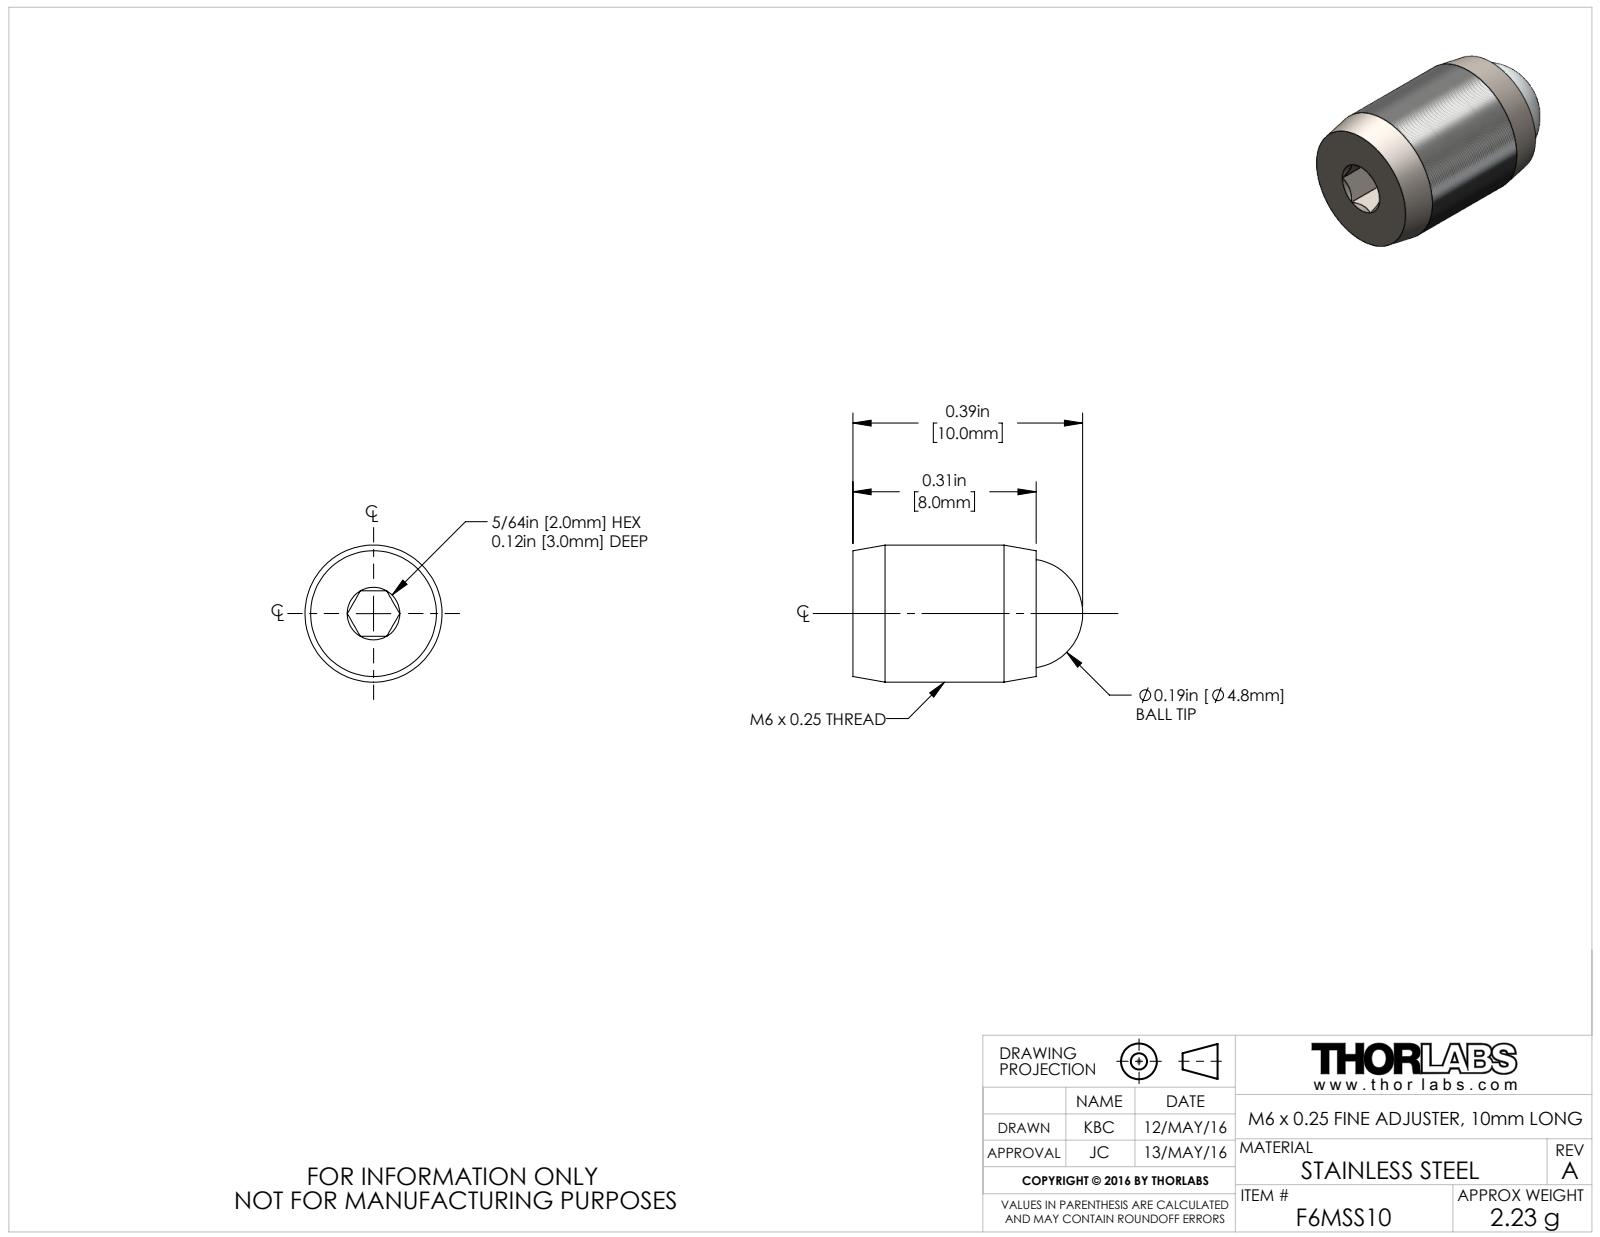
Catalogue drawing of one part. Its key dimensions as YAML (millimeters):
part_name: "TTN102861-E0W"
step_written_by: "SolidWorks 2016 (CONFIG_CONTROL_DESIGN)"
units: millimeters
bodies: {solids: 2, faces: 27, planar: 9, cylindrical: 4, other: 14}
overall_size: [10.03, 5.98, 5.98]
volume: 227
surface_area: 315
round_holes:
  - {diameter: 4.78, count: 1}
round_bosses_or_shafts:
  - {diameter: 5.98, count: 1}
face_to_face_distances: [1.98, 8, 3.05, 4.95]
